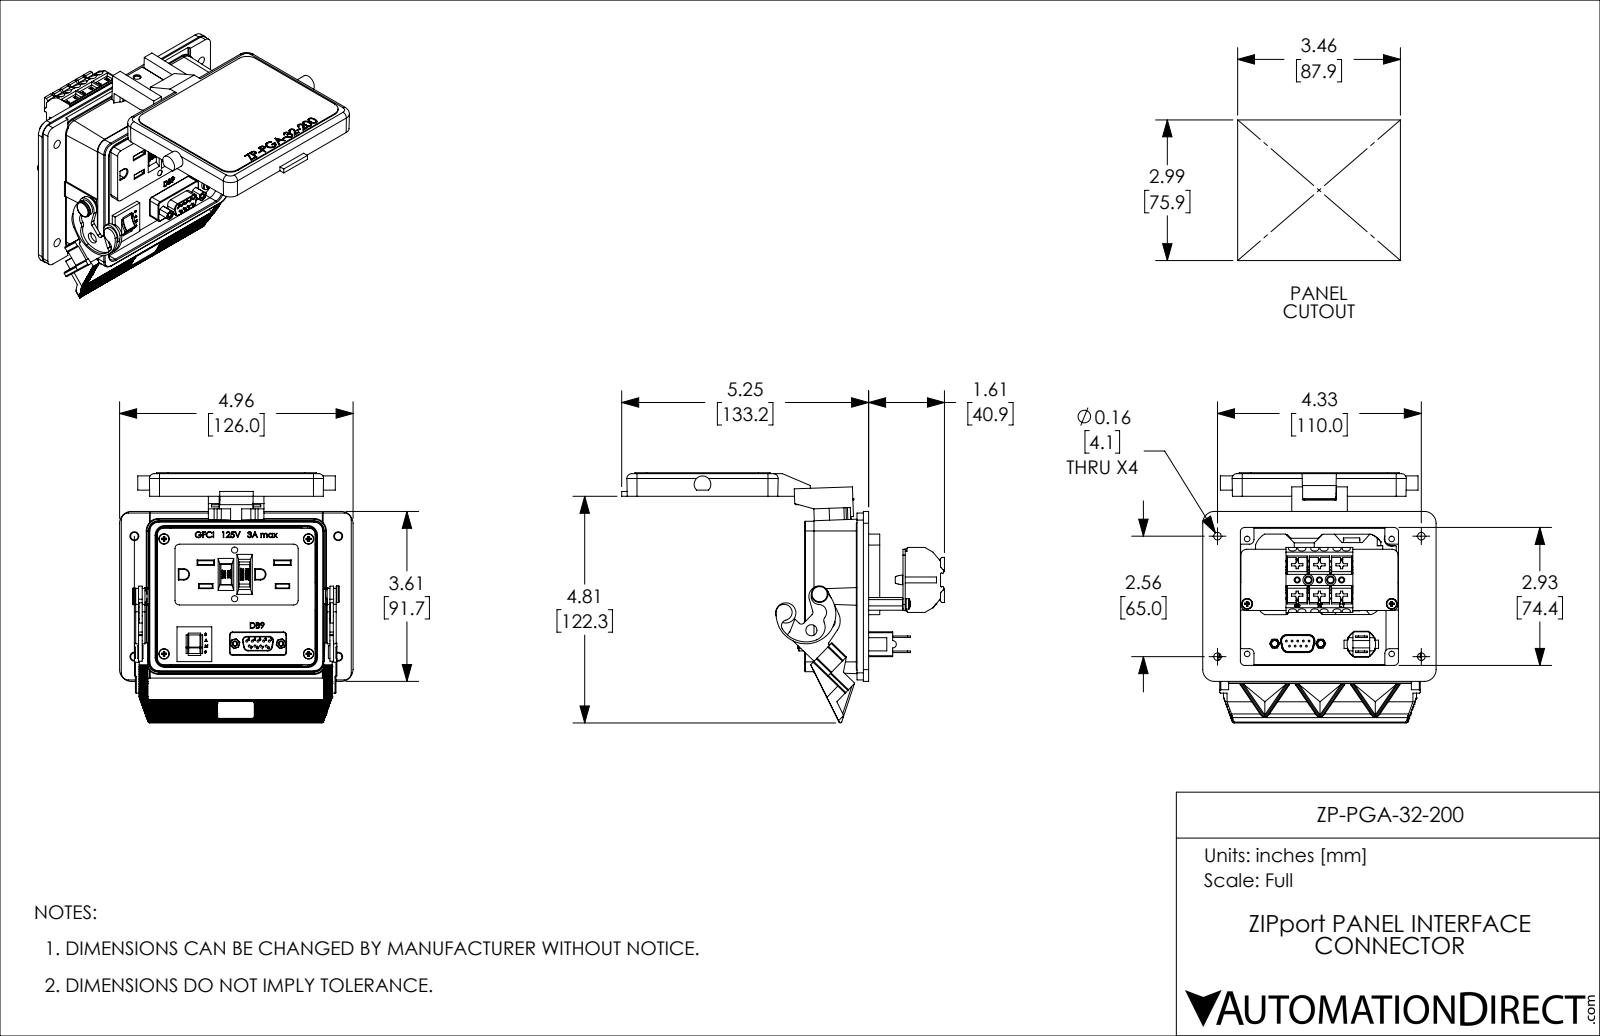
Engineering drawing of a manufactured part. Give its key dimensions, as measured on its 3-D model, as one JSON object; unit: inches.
{"part_name": "ZP-PGA-32-200", "step_written_by": "SolidWorks 2017 (AUTOMOTIVE_DESIGN)", "units": "inches", "bodies": {"solids": 1, "faces": 3250, "planar": 2104, "cylindrical": 663, "other": 483}, "overall_size": [6.857, 5.313, 4.96], "volume_in3": 16.17, "surface_area_in2": 192.3, "round_holes": [[0.045, 9], [0.144, 8], [0.173, 6], [0.098, 4], [0.13, 4], [0.132, 4], [0.16, 4], [0.19, 4], [0.091, 3], [0.09, 2], [0.097, 2], [0.12, 2]], "round_bosses_or_shafts": [[0.038, 9], [0.22, 6], [0.118, 6], [0.205, 3], [0.354, 2], [0.226, 2], [0.109, 2], [0.096, 2]], "partial_cylinders_radius": [[0.02, 24], [0.1, 18], [0.025, 12], [0.25, 12], [0.015, 11], [0.125, 10], [0.005, 8], [0.012, 8]], "face_to_face_distances": [0.135, 0.048, 1.733, 1.003, 0.955, 0.73, 1.685, 0.494, 0.235, 1.19], "hole_center_spacings": [0.12, 0.472, 1.378, 0.236, 0.633, 1.063, 1.287, 1.569]}
